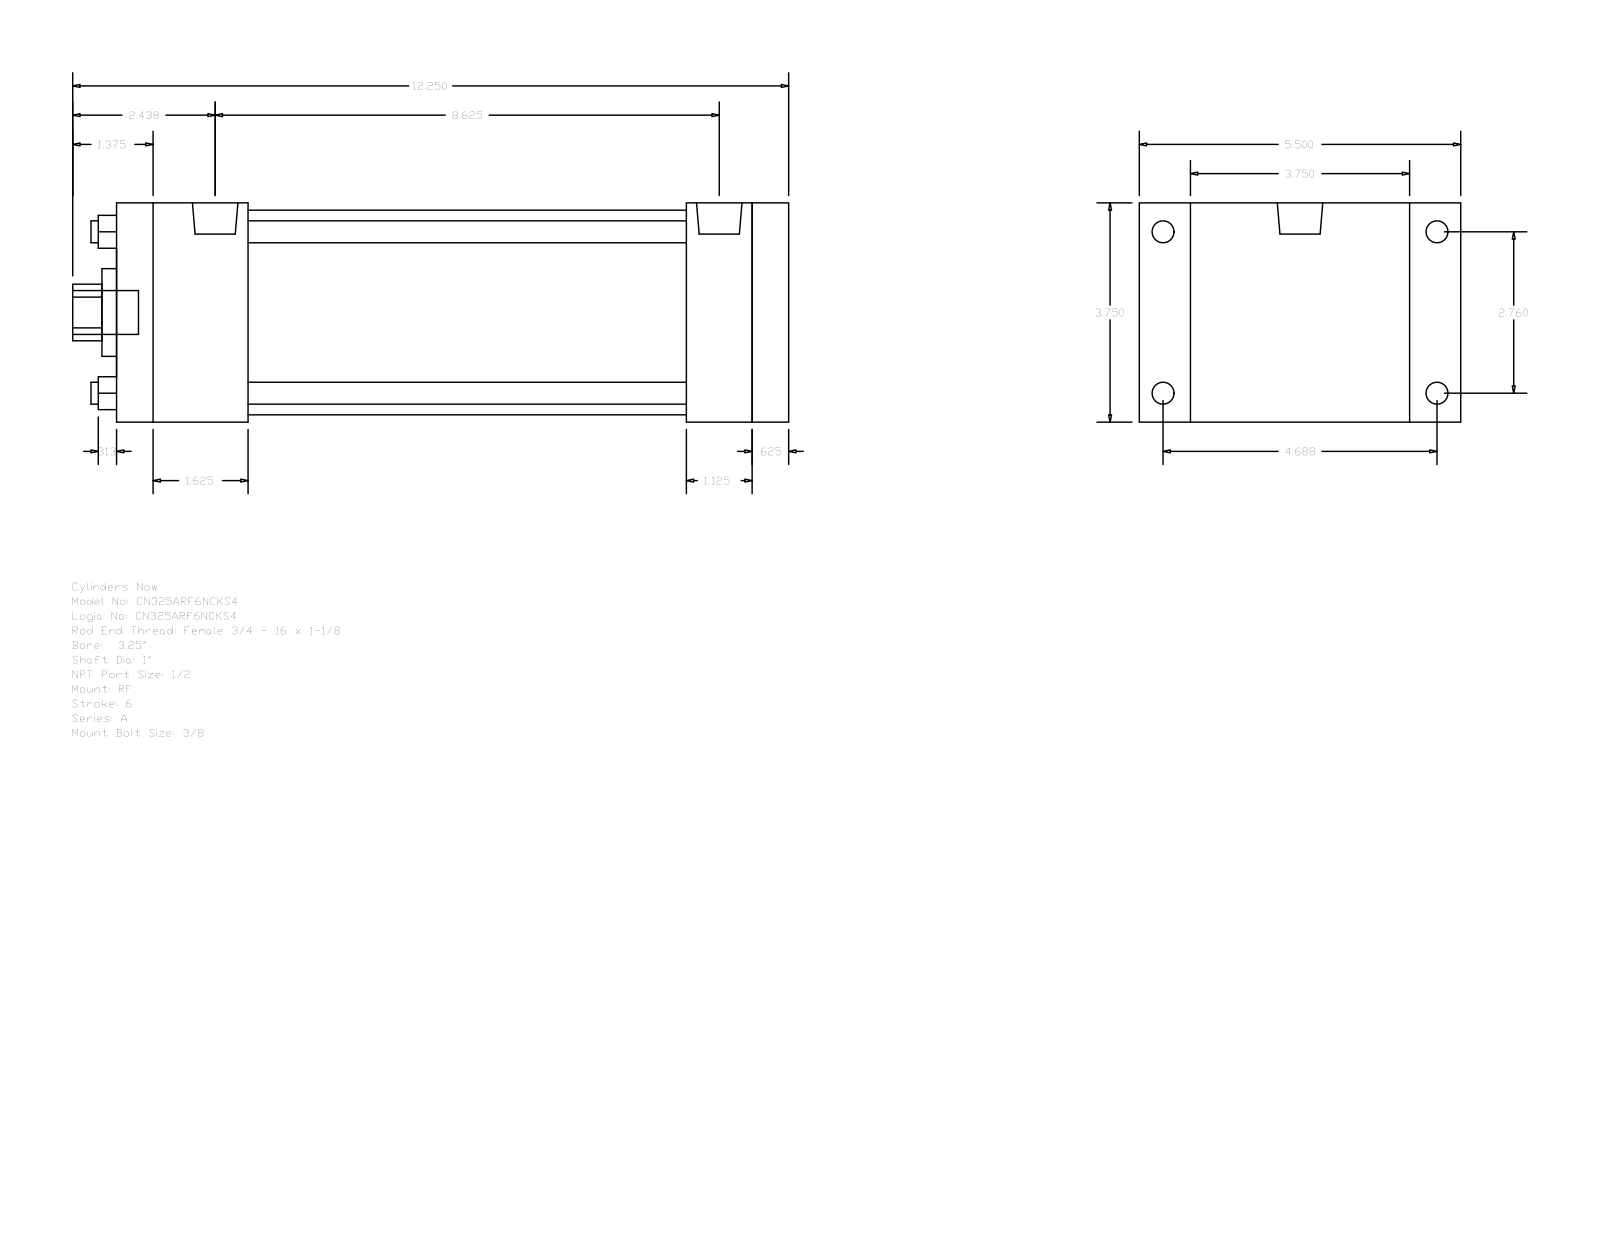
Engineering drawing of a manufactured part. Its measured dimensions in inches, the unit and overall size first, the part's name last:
Units: inches
Overall size (bounding box): 12.25 × 5.5 × 3.75
Round holes (diameter × count): ⌀0.375 ×4, ⌀1 ×1, ⌀1.5 ×1, ⌀3.5 ×1
Round bosses / shafts (diameter × count): ⌀0.375 ×4, ⌀0.344 ×4, ⌀0.778 ×2, ⌀0.75 ×1
Partial cylindrical surfaces — rounded edges, fillets, slot ends (radius × count): R0.484 ×1
Main face-to-face distances: 3.75, 11.5, 10.875, 0.625, 0.875, 4.625, 1.125, 9.75, 1.75, 2.25
Hole centre spacings: 1.952, 2.76, 3.903
Bodies: 0 solids, 92 faces (64 planar, 28 cylindrical, 0 other)
Part name (STEP PRODUCT): A_RF__0325_1
STEP written by: GSSL Pune (CONFIG_CONTROL_DESIGN)
